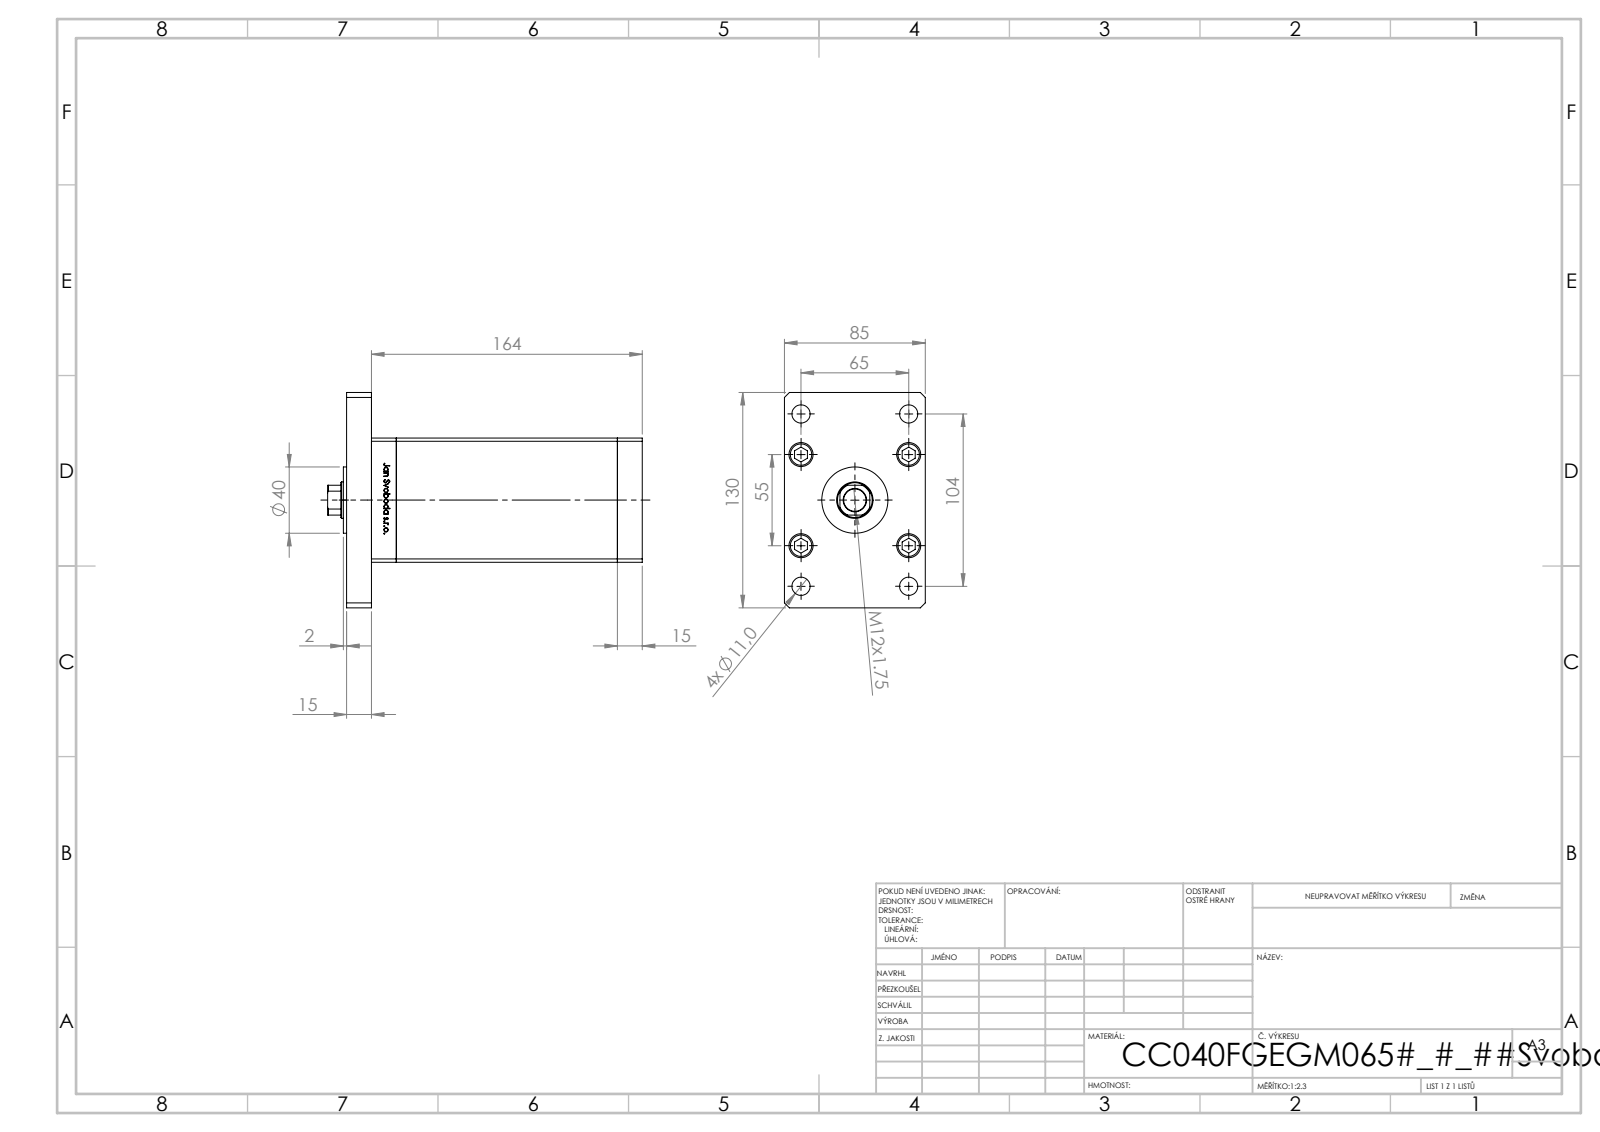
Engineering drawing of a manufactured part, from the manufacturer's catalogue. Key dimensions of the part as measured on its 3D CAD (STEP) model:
Part name (STEP PRODUCT): V220C_F_MIDDLE; ALLEN BOLT; V220C_FRONT_F; V220C BACK_F (+2 more)
STEP written by: SolidWorks 2019 (CONFIG_CONTROL_DESIGN)
Units: millimetres
Bodies: 19 solids, 1310 faces (517 planar, 187 cylindrical, 606 other)
Overall size (bounding box): 190 × 130 × 85
Volume: 1 086 000 mm³ · Surface area: 190 872 mm²
Round holes (diameter × count): ⌀11 ×9, ⌀15.5 ×5, ⌀10 ×4, ⌀14.5 ×4, ⌀2 ×2, ⌀13.16 ×2, ⌀13.5 ×1, ⌀22 ×1, ⌀23.5 ×1
Round bosses / shafts (diameter × count): ⌀8 ×9, ⌀14.5 ×5, ⌀40 ×1
Partial cylindrical surfaces — rounded edges, fillets, slot ends (radius × count): R0.93 ×2, R10.5 ×1
Main face-to-face distances: 15, 148.5, 163.5, 85, 75, 30, 133.5, 178.5, 27.5, 10.5
Hole centre spacings: 28, 24.5, 42.57, 61.32, 65, 69.46, 79.5, 102.69
